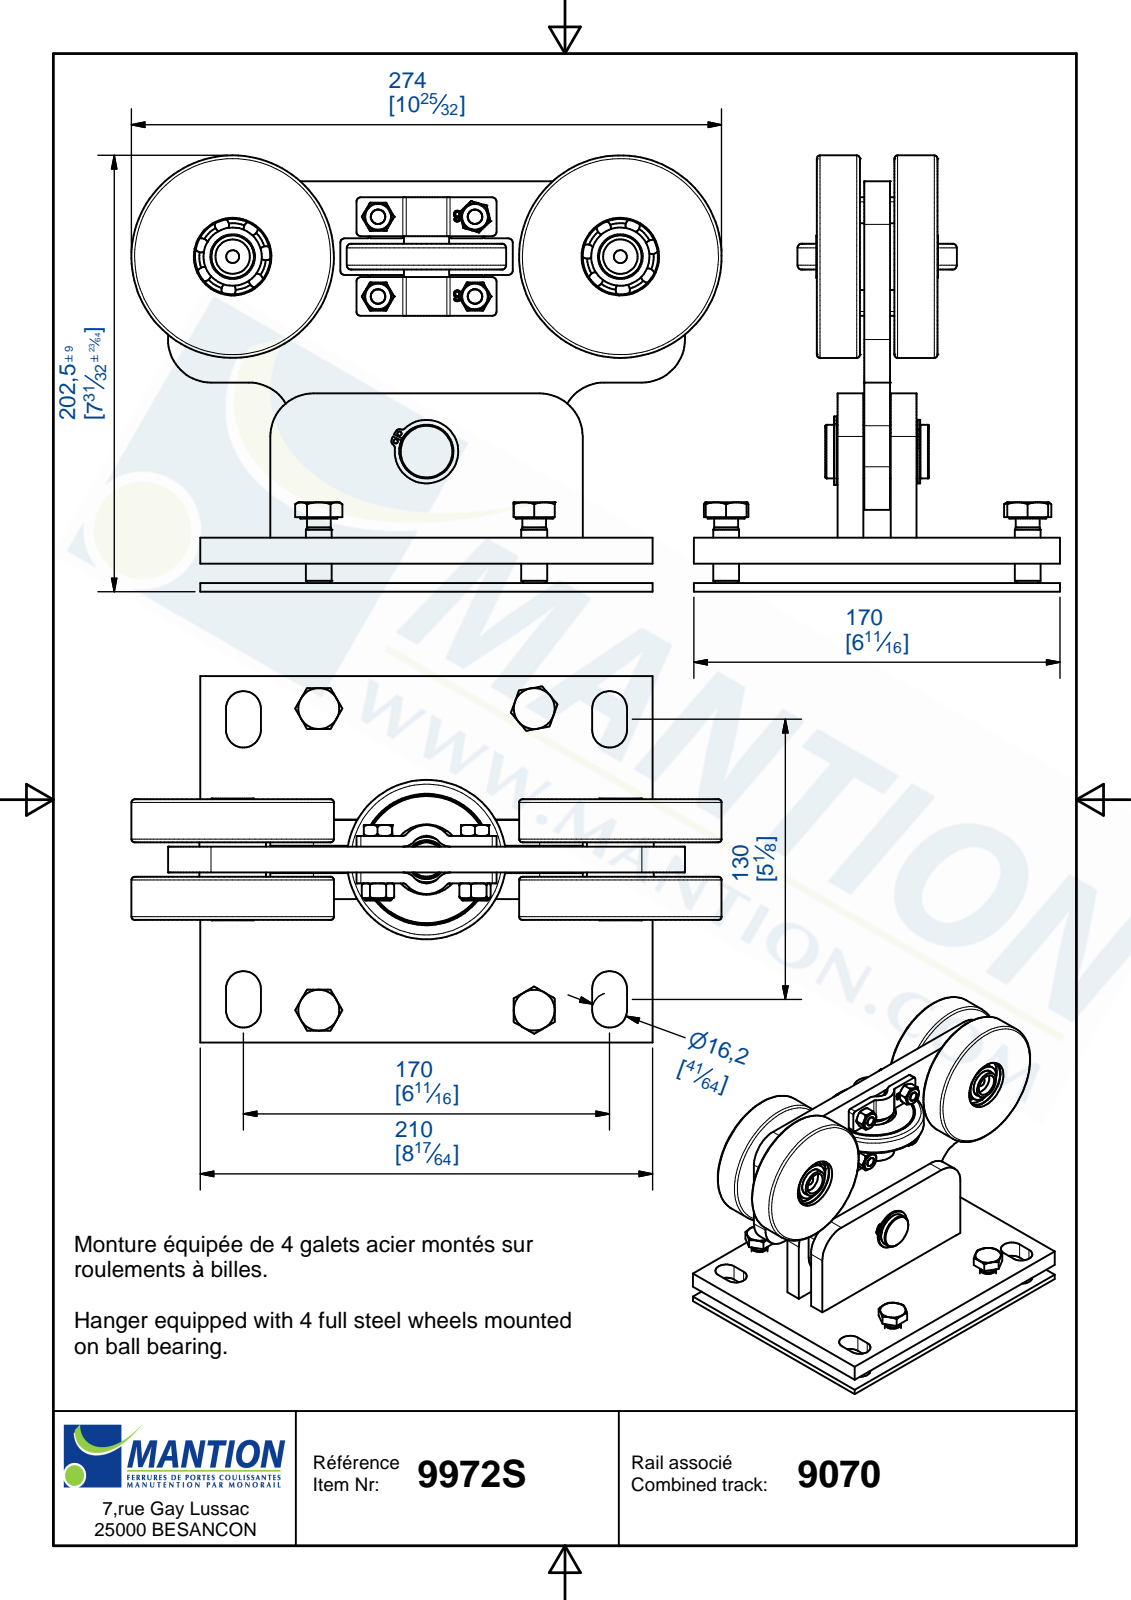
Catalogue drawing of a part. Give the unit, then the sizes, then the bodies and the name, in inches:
Units: inches
Overall size (bounding box): 10.787 × 7.972 × 6.693
Round holes (diameter × count): ⌀0.098 ×8, ⌀0.079 ×4, ⌀0.262 ×4, ⌀0.335 ×4, ⌀0.354 ×4, ⌀0.404 ×4, ⌀0.996 ×3, ⌀0.236 ×2, ⌀0.63 ×2, ⌀0.787 ×2, ⌀0.807 ×2, ⌀1.376 ×2
Round bosses / shafts (diameter × count): ⌀0.677 ×4, ⌀0.492 ×4, ⌀0.472 ×4, ⌀0.435 ×4, ⌀0.315 ×4, ⌀0.984 ×3, ⌀3.701 ×2, ⌀1.752 ×2
Partial cylindrical surfaces — rounded edges, fillets, slot ends (radius × count): R0.079 ×24, R0.02 ×16, R0.098 ×16, R0.787 ×10, R0.319 ×8, R0.059 ×5, R0.039 ×4, R0.276 ×4
Main face-to-face distances: 0.472, 0.486, 0.827, 0.157, 0.512, 0.984, 0.354, 1.417, 0.079, 0.551
Hole centre spacings: 0.76, 2.756, 4.489, 5.167, 0.565, 0.674, 7.087, 0.157
Volume: 104.5 in³ · Surface area: 717.6 in²
Bodies: 45 solids, 990 faces (359 planar, 284 cylindrical, 347 other)
Part name (STEP PRODUCT): 9972S; 18747; 18751; 18755 (+8 more)
STEP written by: Autodesk Inventor 2019 (AUTOMOTIVE_DESIGN)
